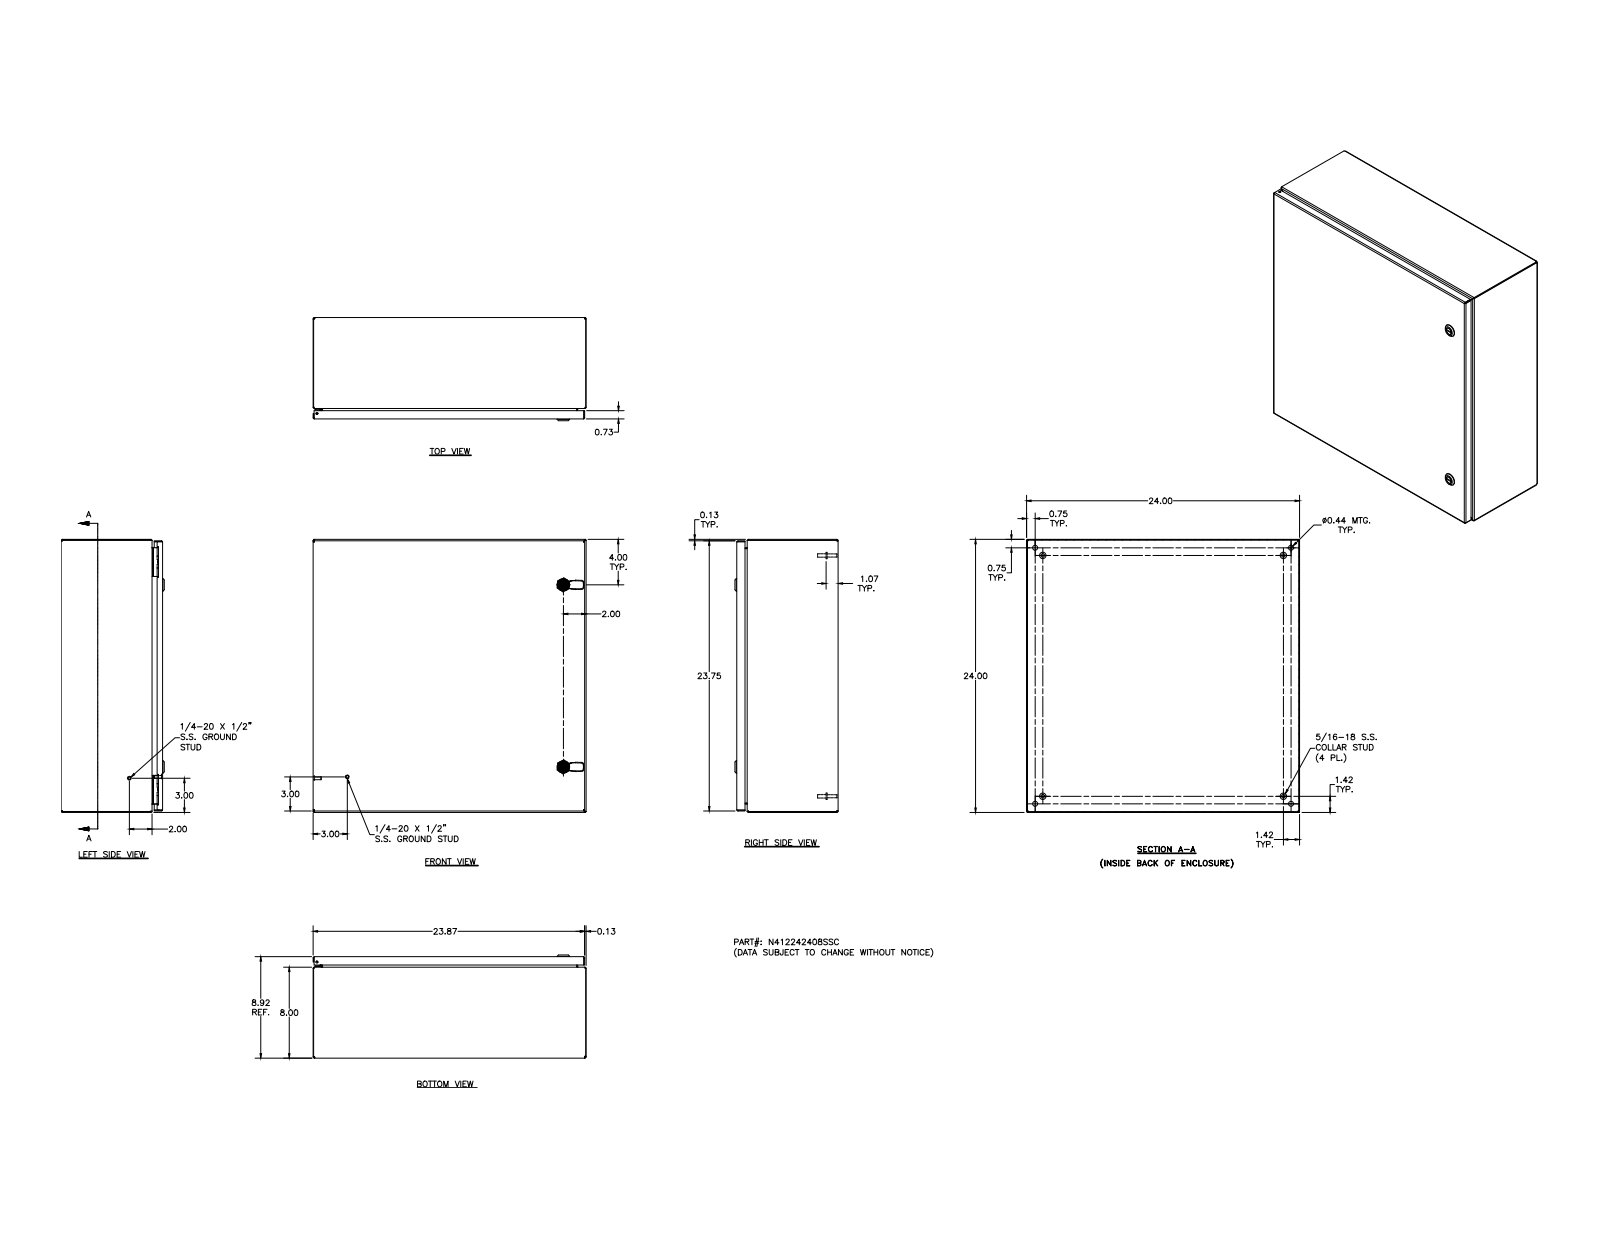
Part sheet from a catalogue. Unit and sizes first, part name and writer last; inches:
Units: inches
Overall size (bounding box): 24 × 24 × 9.075
Round holes (diameter × count): ⌀0.188 ×5, ⌀0.093 ×4, ⌀0.152 ×4, ⌀0.167 ×4, ⌀0.172 ×4, ⌀0.437 ×4, ⌀0.156 ×2, ⌀0.197 ×2, ⌀0.315 ×2, ⌀0.394 ×2, ⌀0.402 ×2, ⌀0.634 ×2
Round bosses / shafts (diameter × count): ⌀0.25 ×10, ⌀0.563 ×4, ⌀0.36 ×4, ⌀0.32 ×4, ⌀0.3 ×4, ⌀0.275 ×4, ⌀0.256 ×4, ⌀0.164 ×4
Partial cylindrical surfaces — rounded edges, fillets, slot ends (radius × count): R0.031 ×30, R0.05 ×26, R0.105 ×20, R0.016 ×18, R0.02 ×15, R0.125 ×14, R0.032 ×8, R0.07 ×8
Main face-to-face distances: 0.074, 8.843, 23.926, 8.917, 8.769, 24, 23.852, 7.926, 0.917, 0.739
Hole centre spacings: 20, 0.017, 0.66, 22.5, 22.869, 0.019, 0.5, 0.648
Volume: 157 in³ · Surface area: 4 260 in²
Bodies: 42 solids, 1682 faces (706 planar, 600 cylindrical, 376 other)
Part name (STEP PRODUCT): N412242408SSC; N412242408SSCBKP; 388151; N4122424SSCLID (+8 more)
STEP written by: Autodesk Inventor 2011 (AUTOMOTIVE_DESIGN)
